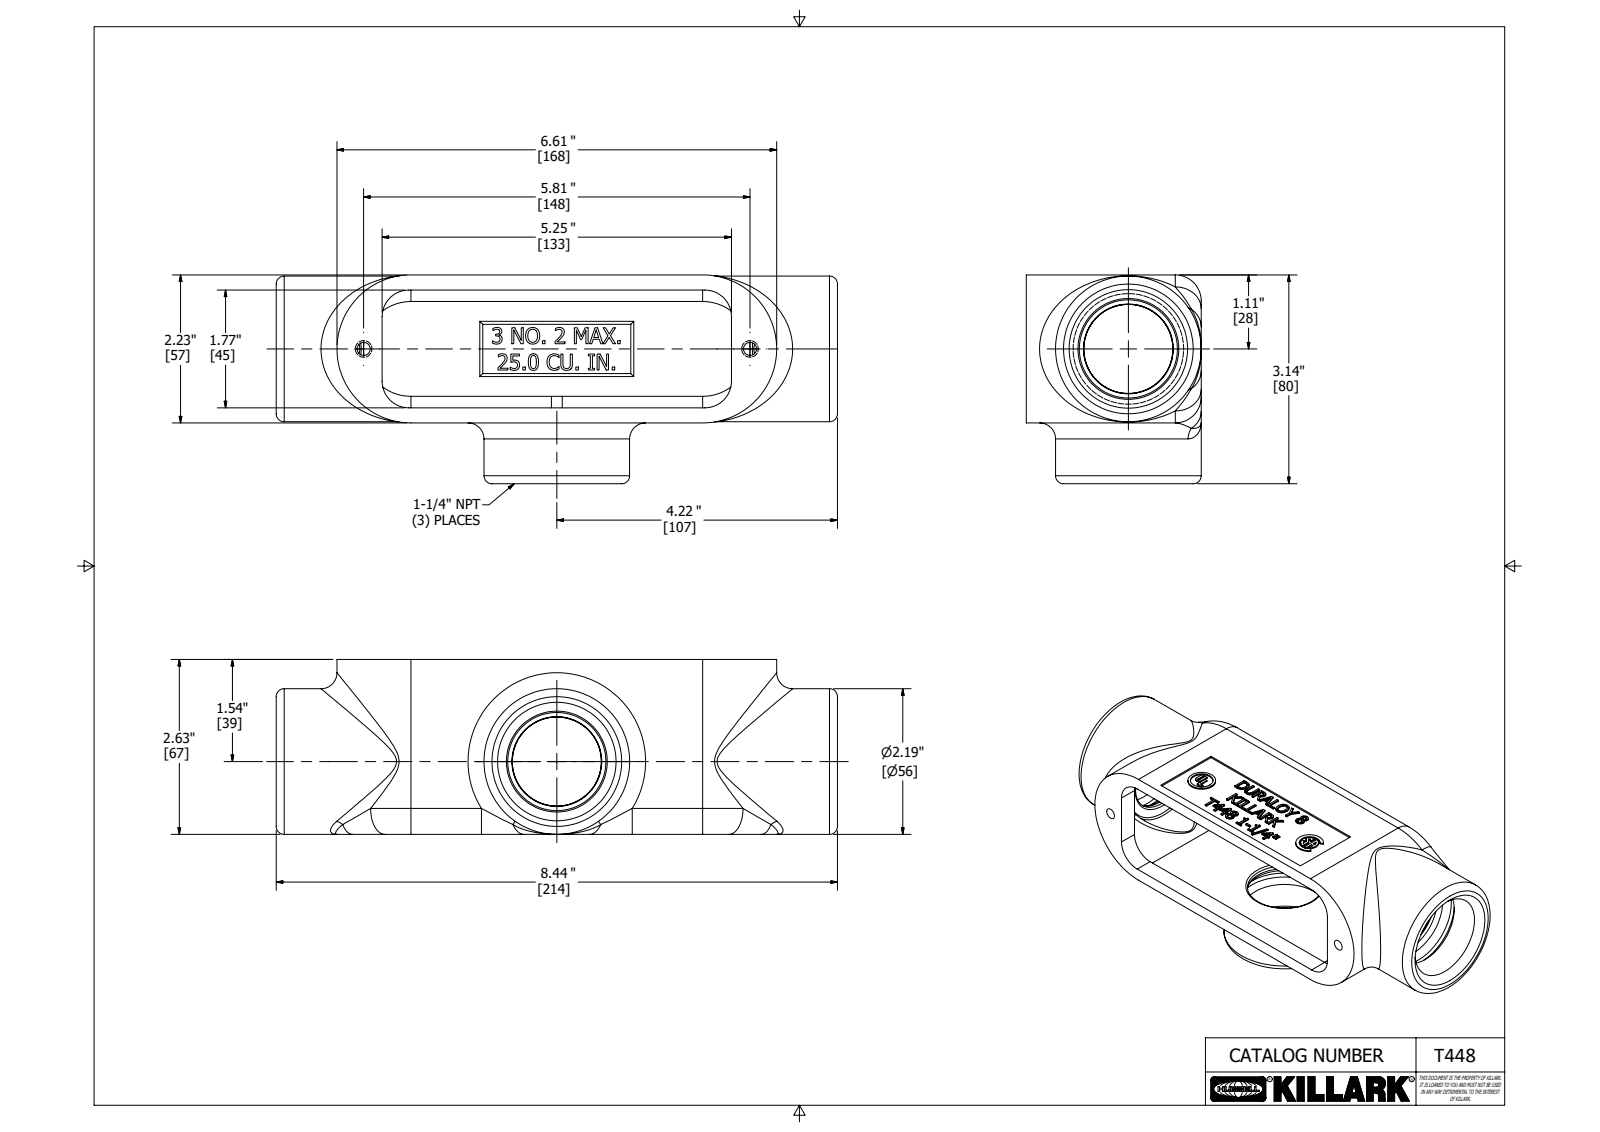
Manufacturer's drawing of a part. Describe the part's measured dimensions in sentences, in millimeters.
The part is named "21743-2". Its 3-D file was written by "Autodesk Inventor 2018 (AUTOMOTIVE_DESIGN)". It is 1 solid with 740 faces: 452 planar, 38 cylindrical and 250 other. Overall it measures 214.4 by 79.7 by 66.8 millimeters. Its volume is 246 800 cubic millimeters and its surface area 86 450 square millimeters. Round holes: 2 of diameter 5, 2 of diameter 42.3, 1 of diameter 10.3, 1 of diameter 45.2. Round bosses or shafts: 2 of diameter 55.6, 1 of diameter 12.7. Partial cylindrical surfaces (rounded edges, fillets, slot ends): 4 of radius 10.2, 2 of radius 5.1, 2 of radius 9.9, 2 of radius 23.2, 2 of radius 28.3, 1 of radius 0.4, 1 of radius 1.6, 1 of radius 2.9. The main face-to-face distances are 5.1, 51.4, 46.4, 56.5, 66.8, 61.7, 0.8, 55.8, 50.7, 4.3. The hole center spacings are 39.7, 147.6.
